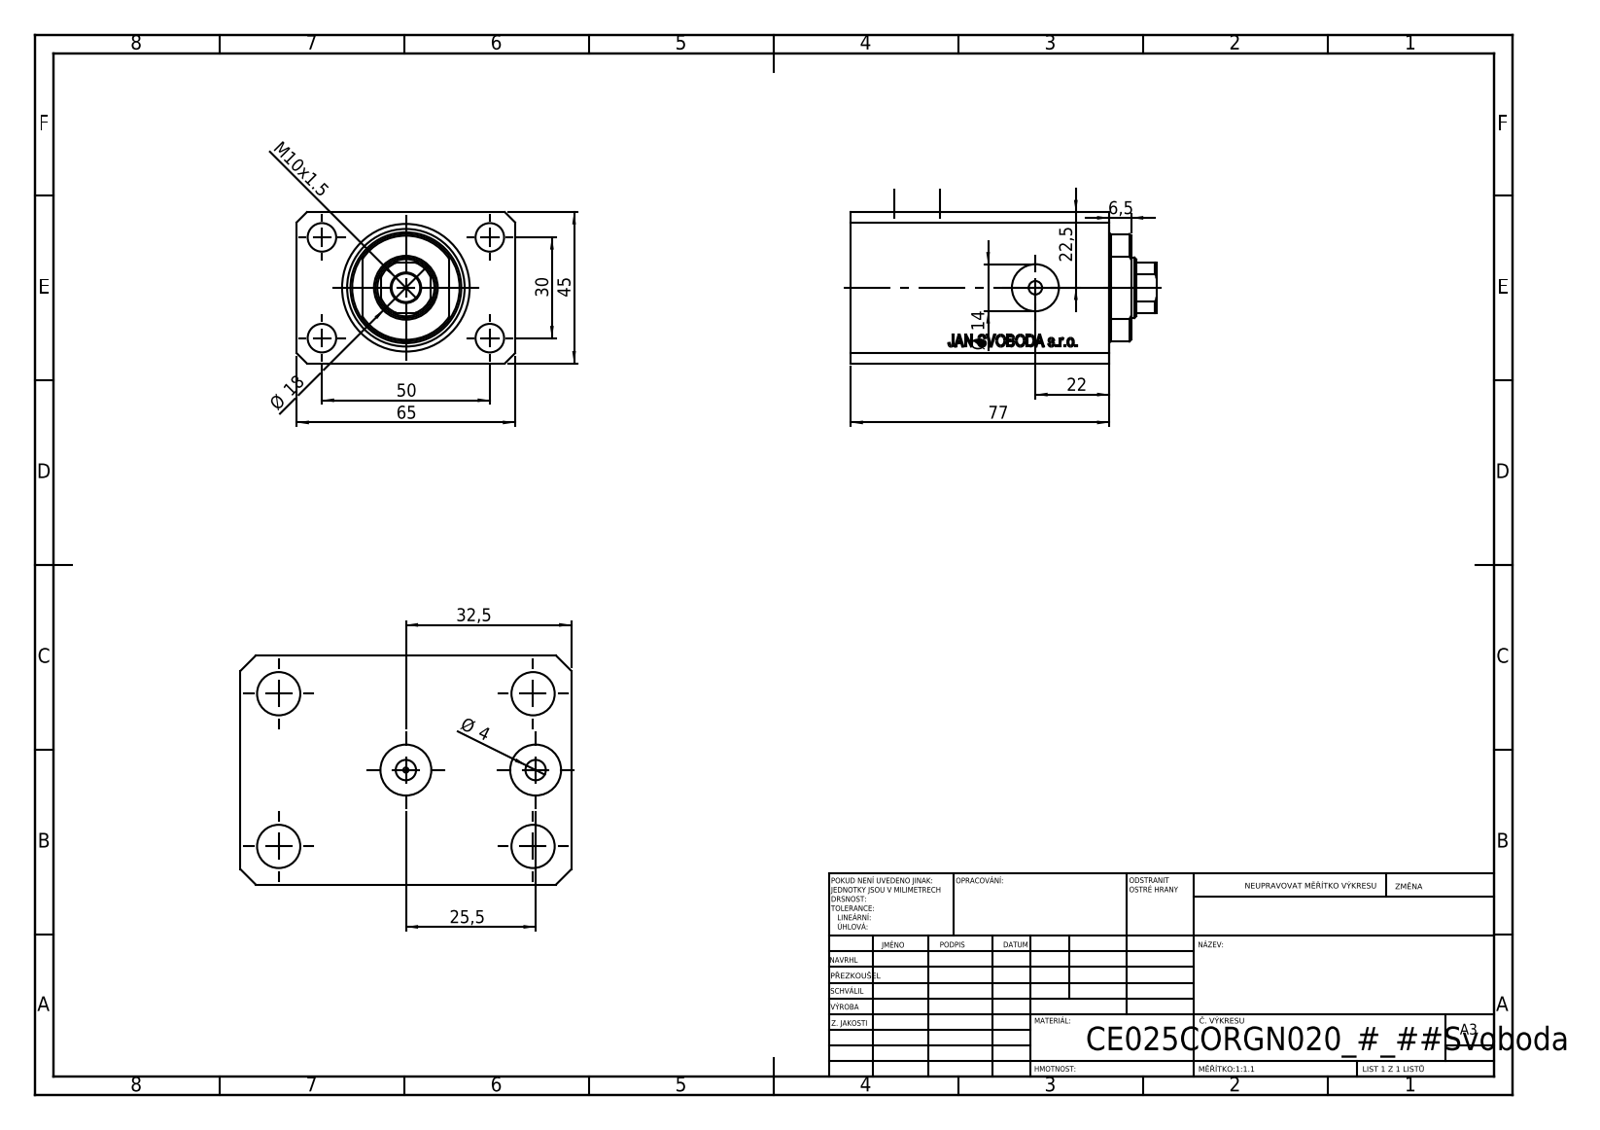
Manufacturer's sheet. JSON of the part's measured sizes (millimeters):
{"part_name": "V250CE_VC_C; V250CE_C_VCP; V250CE_C_Body", "step_written_by": "SolidWorks 2019 (CONFIG_CONTROL_DESIGN)", "units": "millimeters", "bodies": {"solids": 3, "faces": 872, "planar": 428, "cylindrical": 50, "other": 394}, "overall_size": [91, 65, 45], "volume_mm3": 203440, "surface_area_mm2": 50754, "round_holes": [[8.5, 5], [4, 4], [10, 2], [14, 2], [1.25, 1], [18, 1], [25, 1], [38, 1]], "partial_cylinders_radius": [[8.5, 1], [16, 1]], "face_to_face_distances": [45, 65, 14, 77, 63, 6.9, 56.1, 70.1, 73.52, 20.5], "hole_center_spacings": [29.15, 15.01, 30, 50, 52.68, 58.31, 25.5, 33]}
